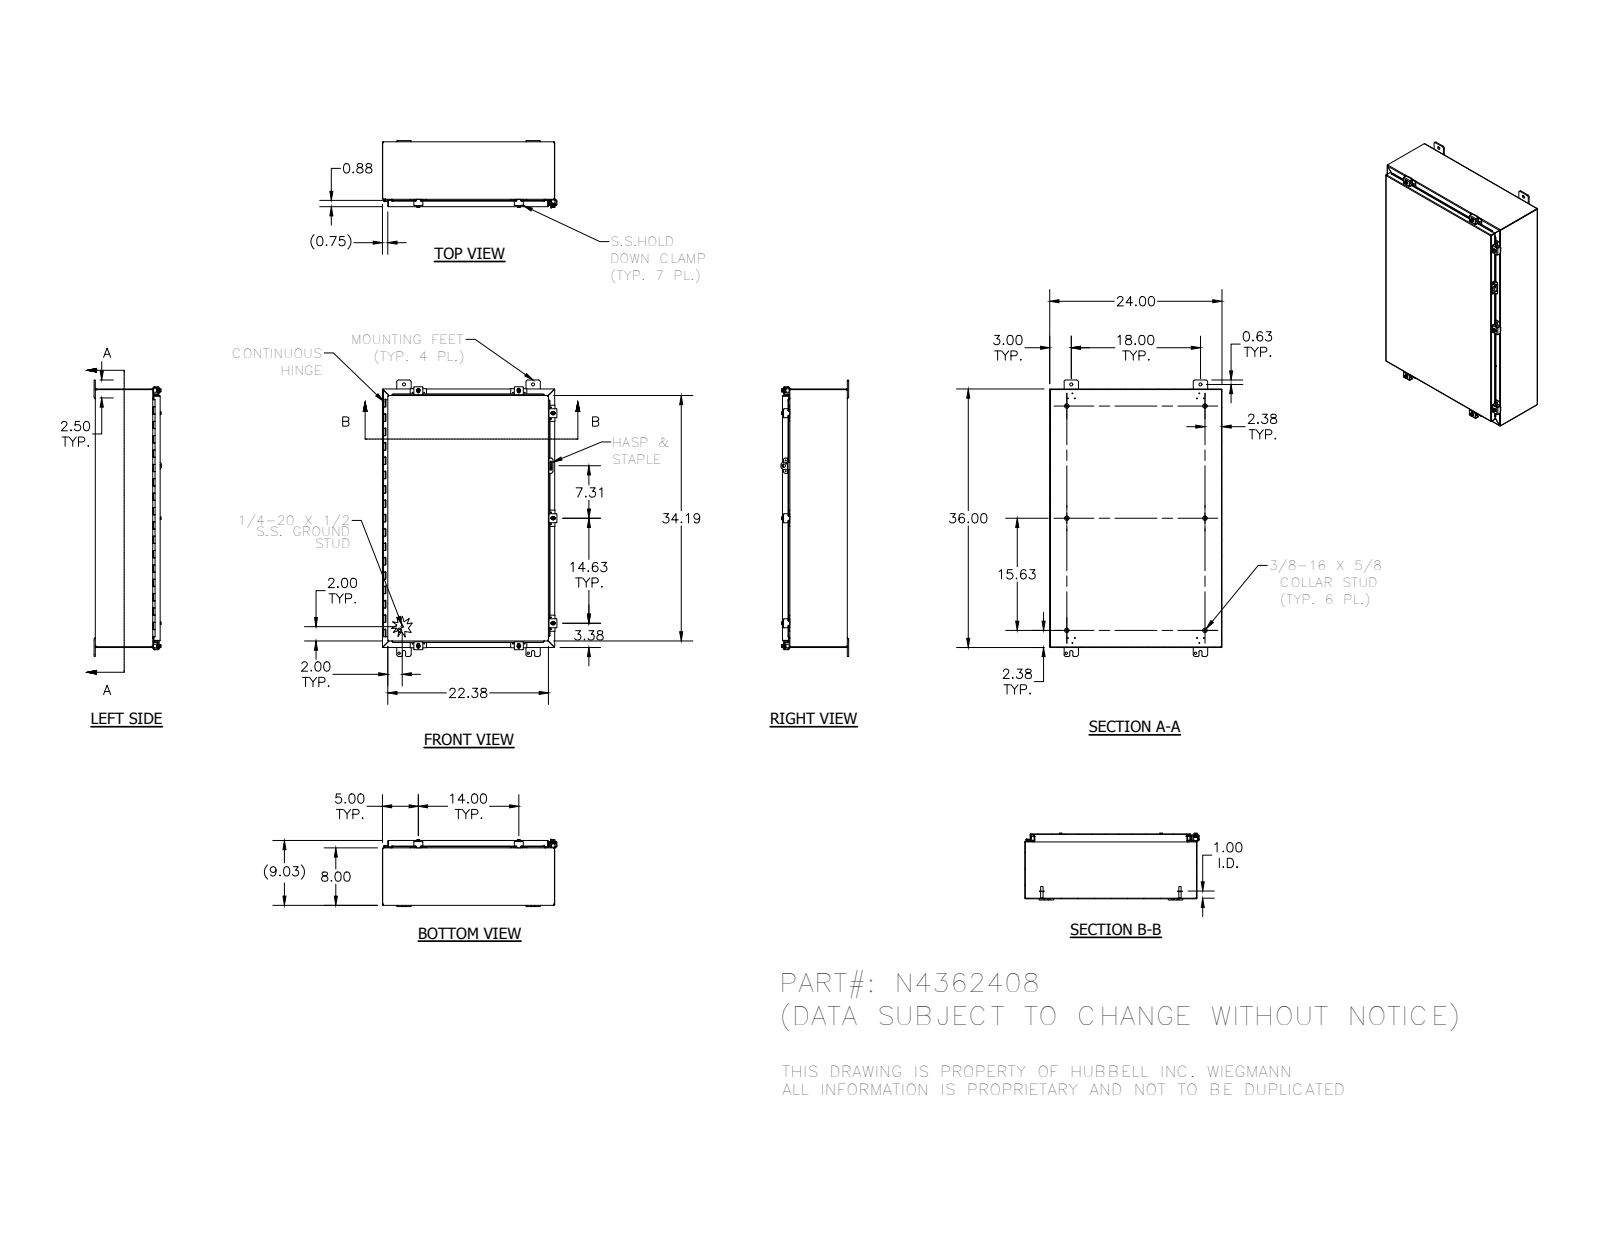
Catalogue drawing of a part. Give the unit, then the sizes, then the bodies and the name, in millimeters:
Units: millimetres
Overall size (bounding box): 977.9 × 617.5 × 239
Round holes (diameter × count): ⌀2.8 ×17, ⌀3 ×12, ⌀5.4 ×7, ⌀7.1 ×7, ⌀7.6 ×7, ⌀8 ×4, ⌀11.1 ×4, ⌀3.2 ×1, ⌀4 ×1, ⌀12.7 ×1
Round bosses / shafts (diameter × count): ⌀6.4 ×9, ⌀13.2 ×7, ⌀12.7 ×7, ⌀8.9 ×7, ⌀15.9 ×6, ⌀8.4 ×6, ⌀2.9 ×2, ⌀8.6 ×1
Partial cylindrical surfaces — rounded edges, fillets, slot ends (radius × count): R0.8 ×83, R1.6 ×41, R3.2 ×37, R6.4 ×33, R0.8 ×23, R2.7 ×23, R1.6 ×14, R3.6 ×14
Main face-to-face distances: 1.9, 227.6, 225.7, 229.4, 607.7, 912.5, 201.3, 26.2, 605.8, 609.6
Hole centre spacings: 457.2, 22.3, 19.3, 23.9, 24.6, 50.7, 441.2, 465.8
Volume: 3 964 000 mm³ · Surface area: 4 095 000 mm²
Bodies: 54 solids, 2404 faces (930 planar, 1087 cylindrical, 387 other)
Part name (STEP PRODUCT): N4362408BKP_1; 38420_1; 32911_1; N4362408 (+8 more)
STEP written by: SolidWorks 2014 (AUTOMOTIVE_DESIGN)
